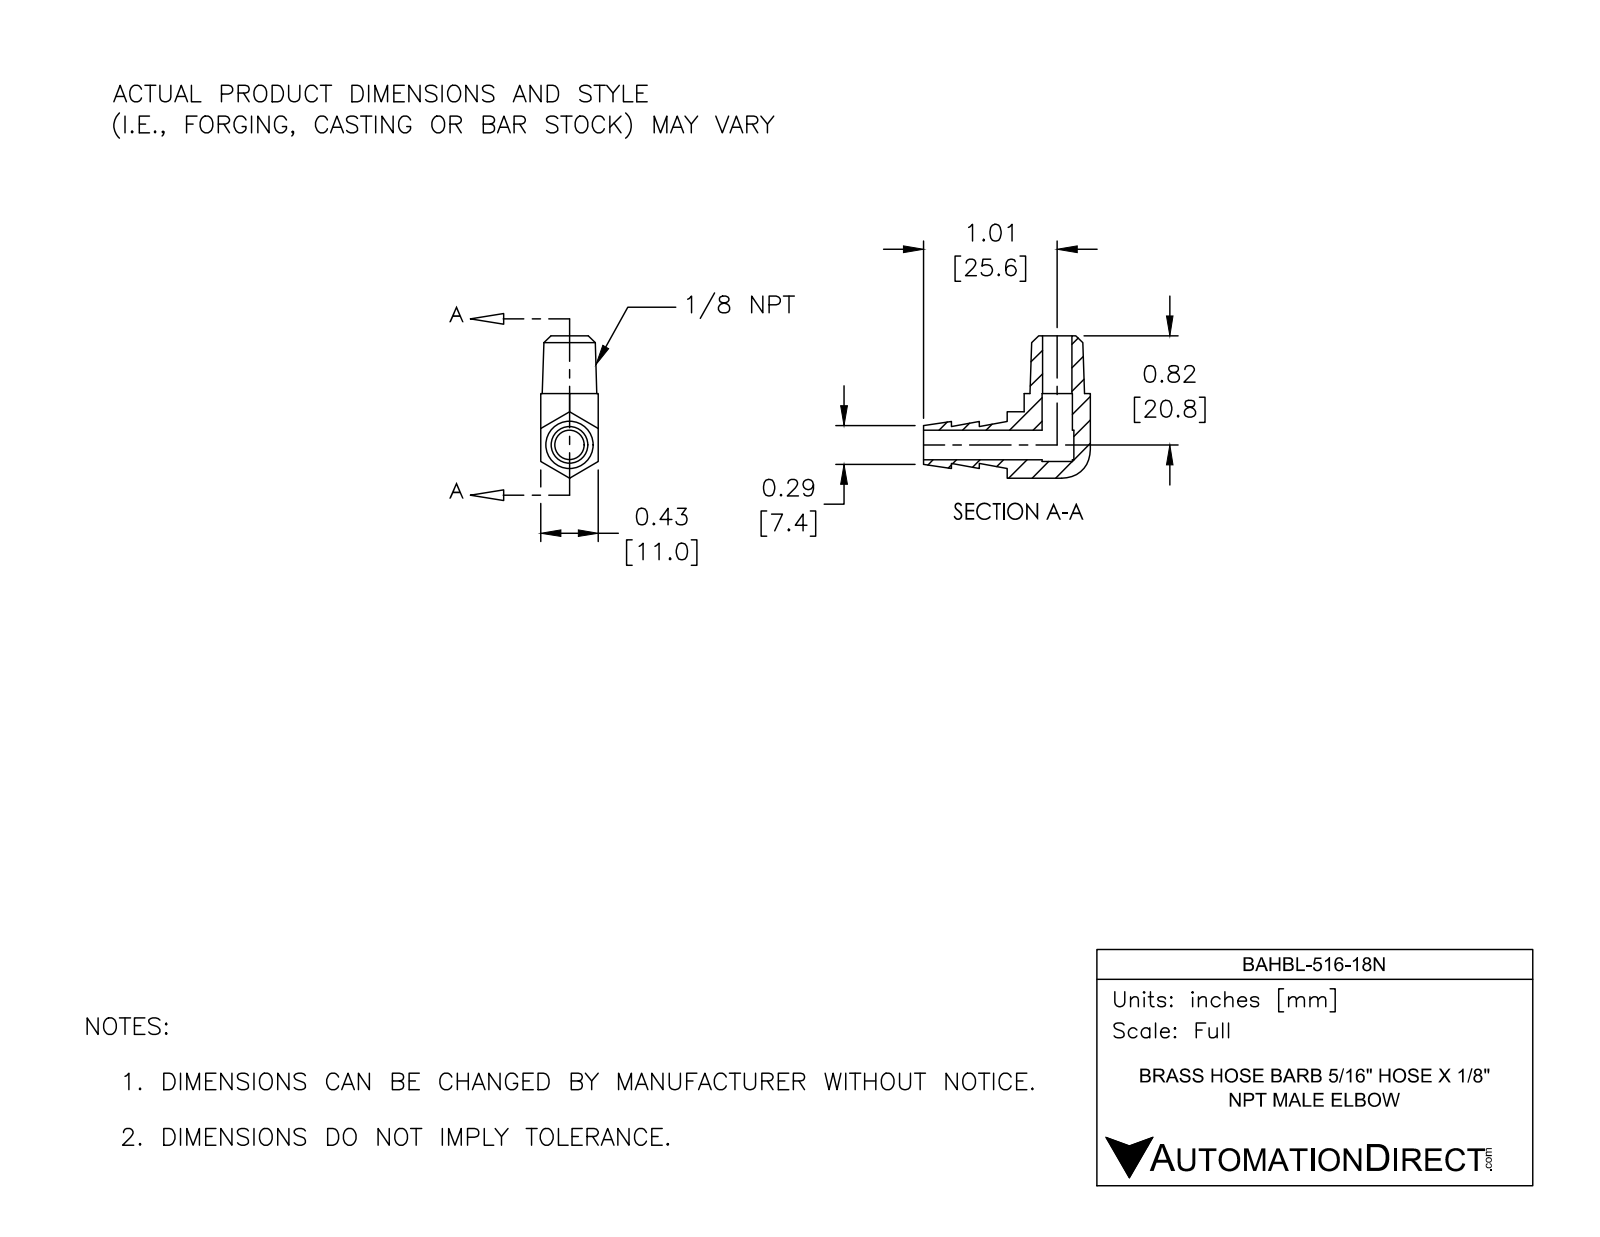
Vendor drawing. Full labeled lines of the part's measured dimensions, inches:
Part name (STEP PRODUCT): BAHBL-516-18N
STEP written by: SolidWorks 2017 (AUTOMOTIVE_DESIGN)
Units: inches
Bodies: 1 solid, 39 faces (19 planar, 10 cylindrical, 10 other)
Overall size (bounding box): 1.256 × 1.07 × 0.432
Volume: 0.147 in³ · Surface area: 3.834 in²
Round holes (diameter × count): ⌀0.222 ×2, ⌀0.227 ×1
Partial cylindrical surfaces — rounded edges, fillets, slot ends (radius × count): R0.25 ×2
Main face-to-face distances: 0.432, 0.432, 0.21, 0.42, 0.502, 0.711, 0.921, 0.511, 0.945, 0.434
